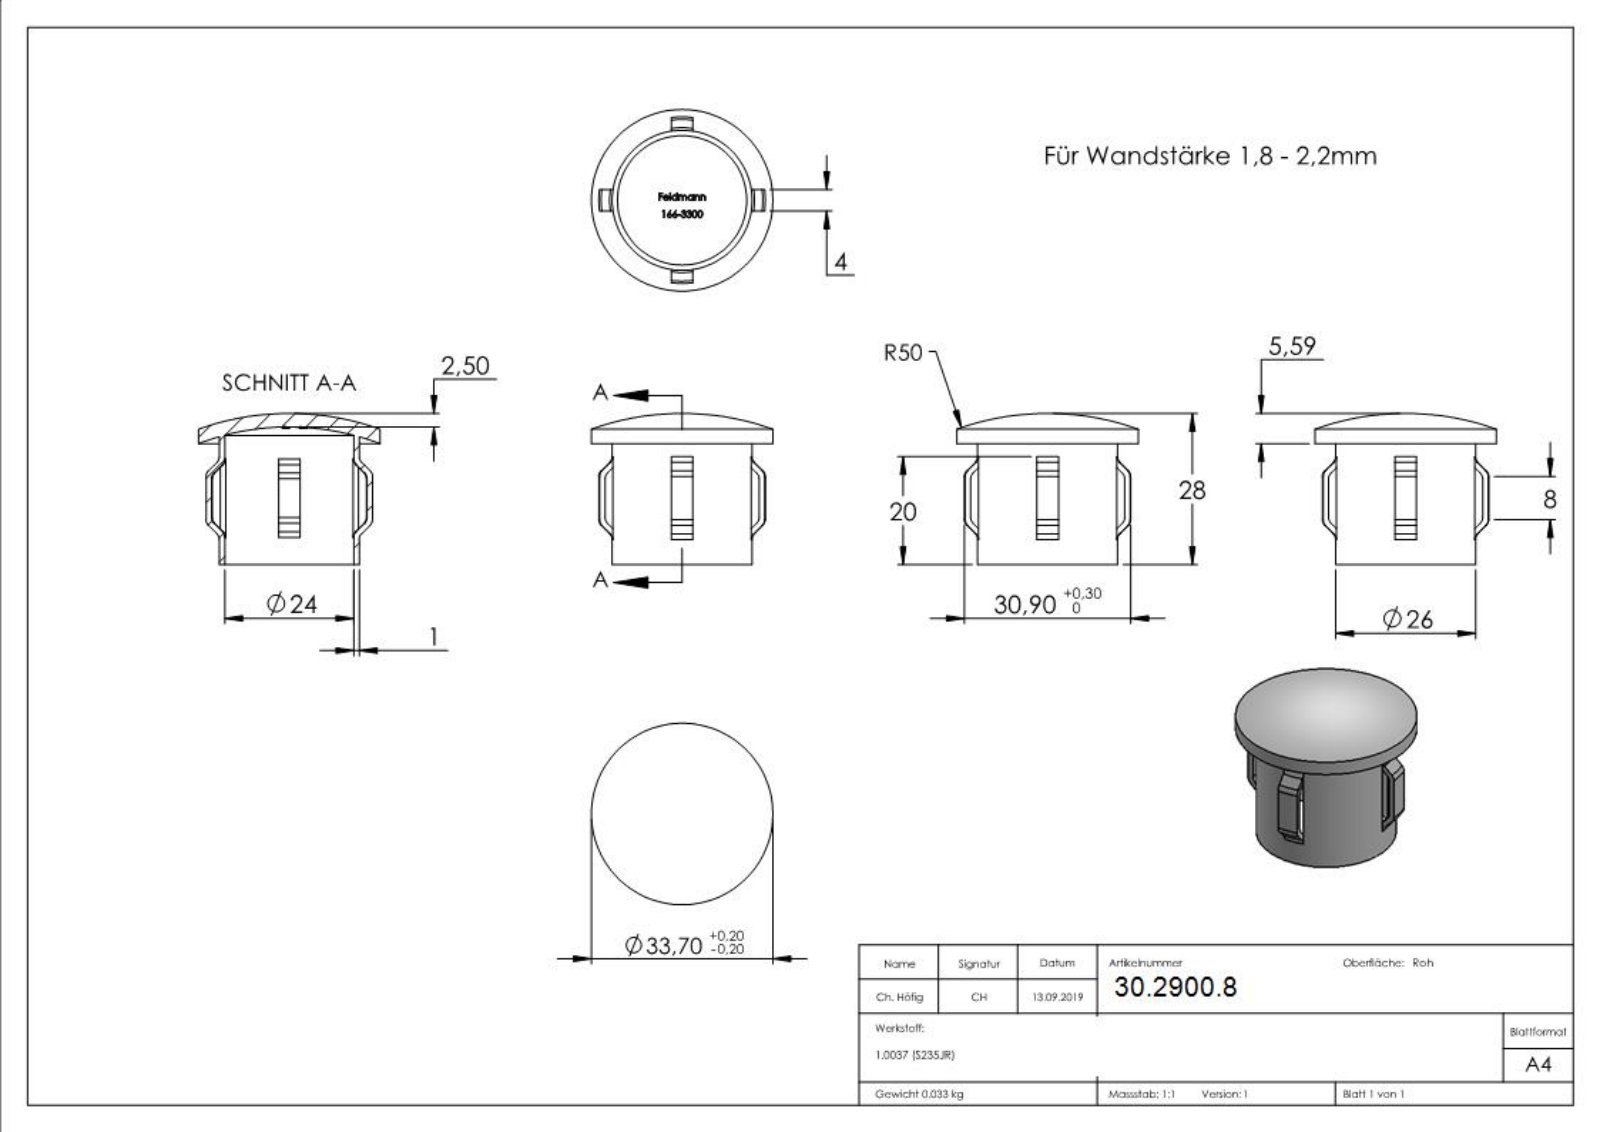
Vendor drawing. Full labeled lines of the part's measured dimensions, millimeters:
Part name (STEP PRODUCT): 166-3300
STEP written by: SolidWorks 2015 (CONFIG_CONTROL_DESIGN)
Units: millimetres
Bodies: 1 solid, 319 faces (93 planar, 16 cylindrical, 210 other)
Overall size (bounding box): 33.7 × 33.7 × 28
Volume: 4 204 mm³ · Surface area: 6 144 mm²
Round holes (diameter × count): ⌀24 ×1
Round bosses / shafts (diameter × count): ⌀33.7 ×1, ⌀26 ×1
Partial cylindrical surfaces — rounded edges, fillets, slot ends (radius × count): R14.45 ×1, R15.45 ×1
Main face-to-face distances: 4, 2.97, 1.26, 2, 0.39, 3.27, 0.87, 0.85, 2.28, 0.99
